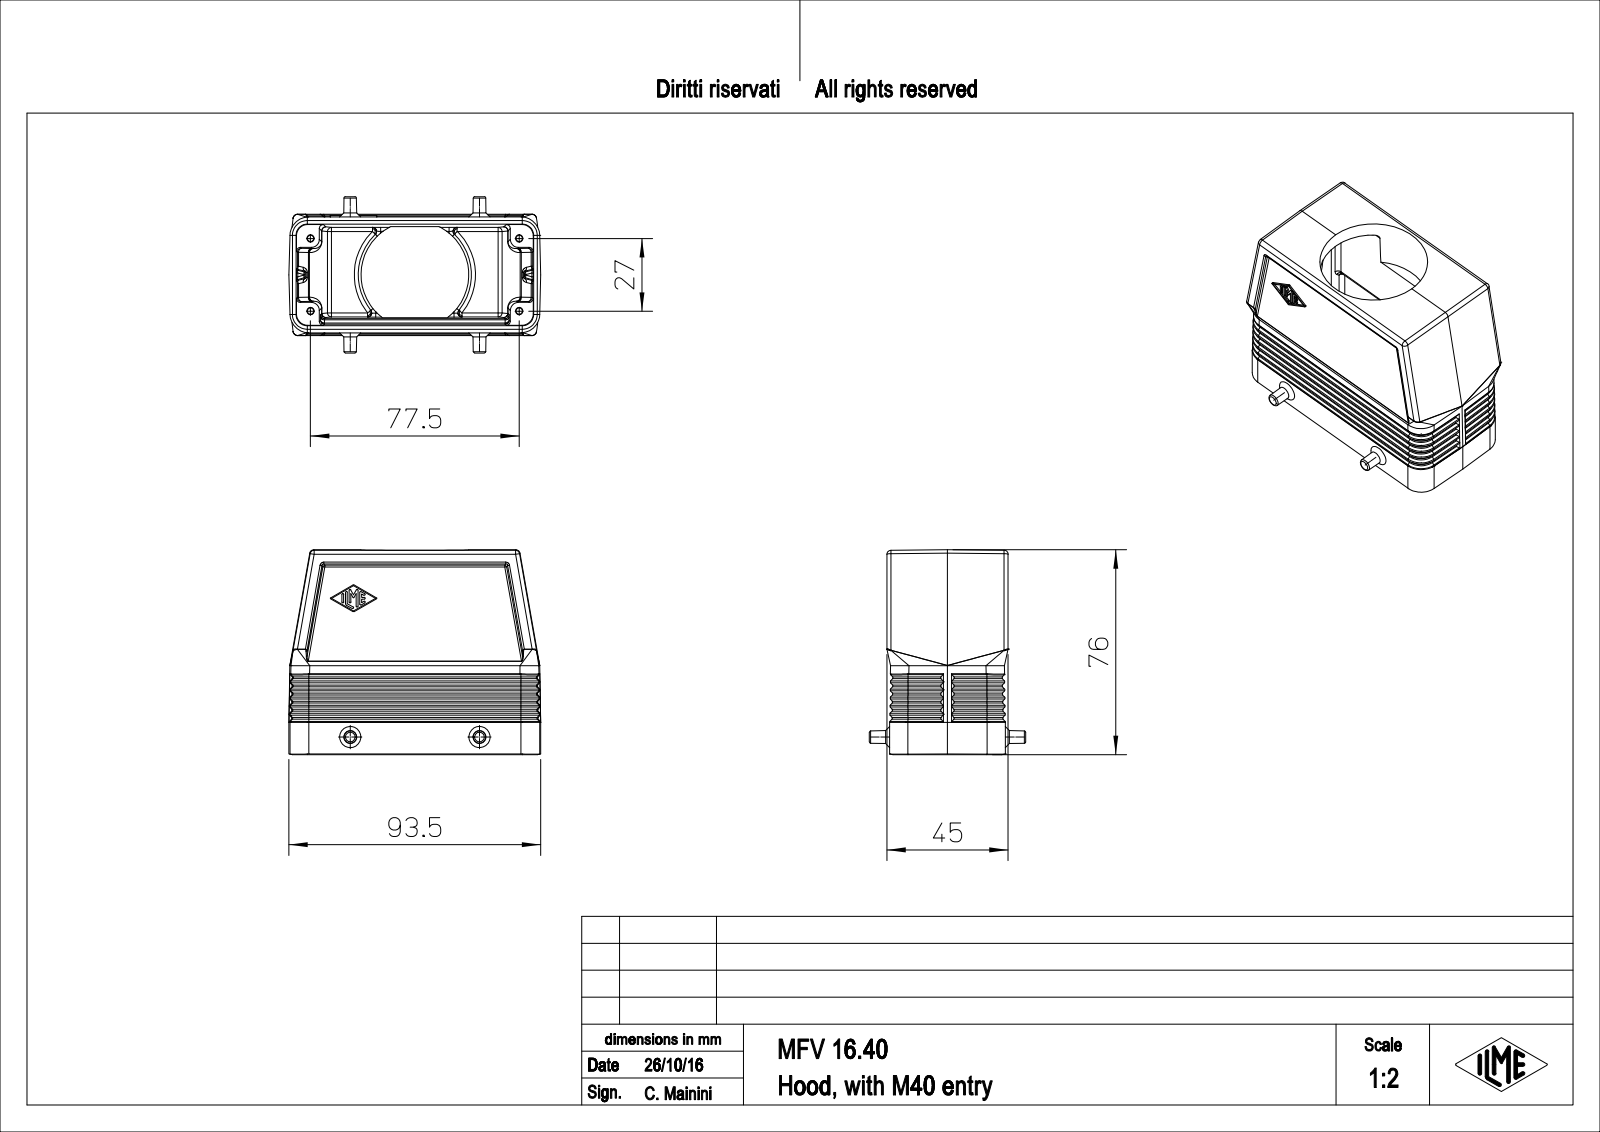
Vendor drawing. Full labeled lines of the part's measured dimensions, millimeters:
Part name (STEP PRODUCT): MFV_16.40
STEP written by: PTC Creo Elements/Direct Modeling 19.0E 27-Jun-2016 (C) Parametric Technology GmbH (AUTOMOTIVE_DESIGN)
Units: millimetres
Bodies: 1 solid, 478 faces (210 planar, 132 cylindrical, 136 other)
Overall size (bounding box): 93.5 × 76 × 58
Volume: 84 982 mm³ · Surface area: 43 063 mm²
Round holes (diameter × count): ⌀2.75 ×4, ⌀40 ×1
Round bosses / shafts (diameter × count): ⌀4.59 ×2
Partial cylindrical surfaces — rounded edges, fillets, slot ends (radius × count): R0.5 ×78, R1.5 ×10, R7 ×8, R3 ×4, R4.2 ×4, R21 ×1
Main face-to-face distances: 43, 2.01, 2, 8.5, 4, 44, 1, 6, 6.01, 4.01
Hole centre spacings: 41.03, 27, 77.5, 82.07
